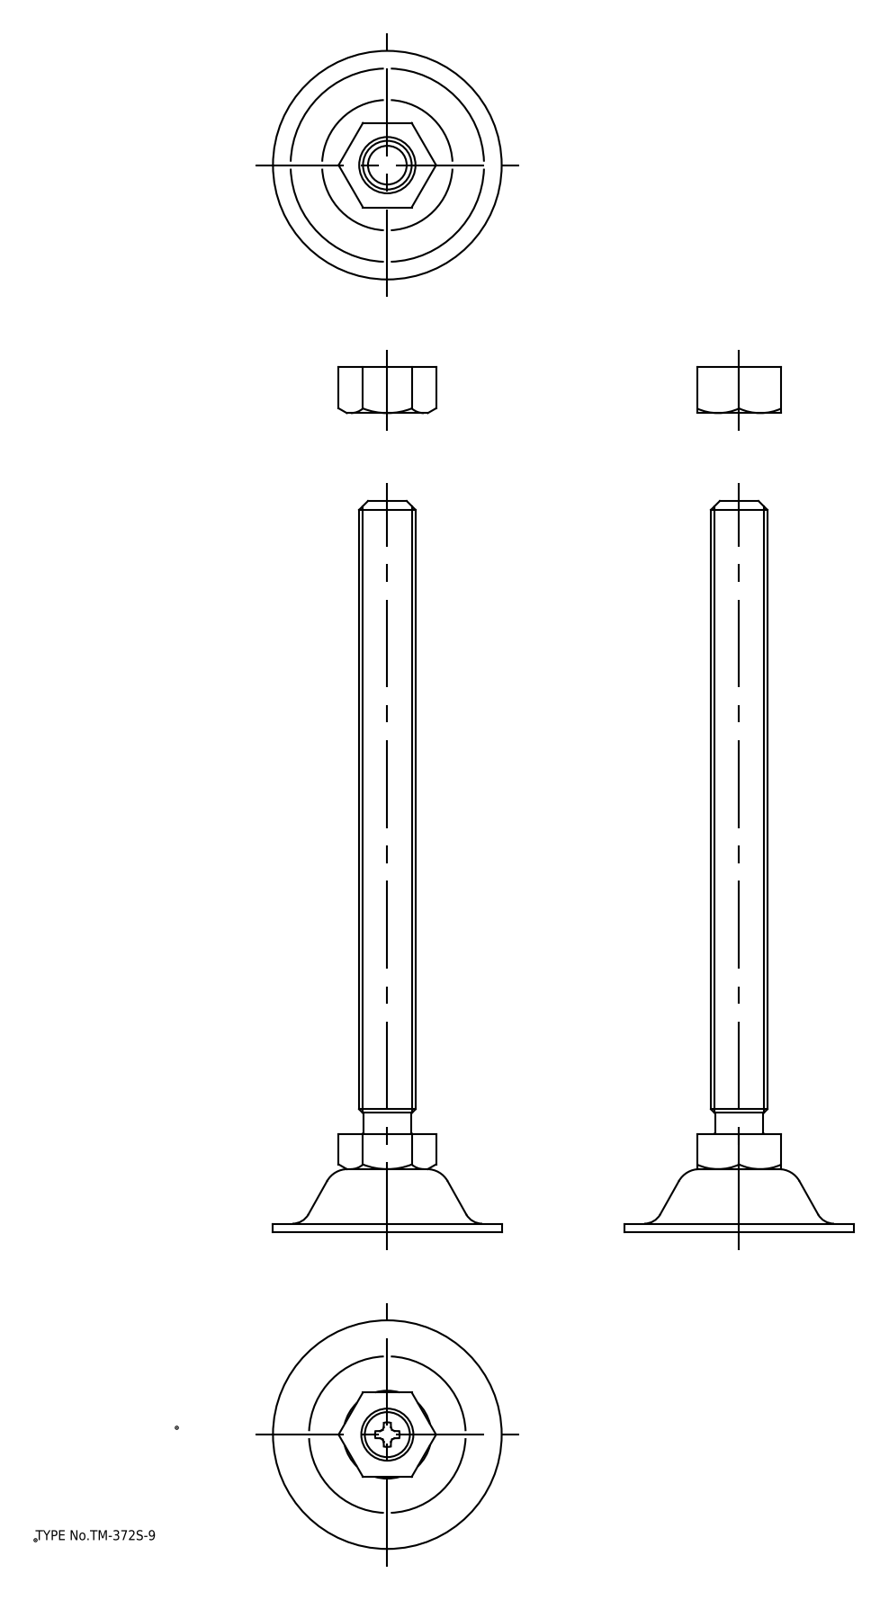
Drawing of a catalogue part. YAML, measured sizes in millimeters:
part_name: "アジャストボルト; ナット; フット"
step_written_by: "spGate 18.9.1 (****-****-****-****) (AUTOMOTIVE_DESIGN)"
units: millimeters
bodies: {solids: 3, faces: 90, planar: 48, cylindrical: 18, other: 24}
overall_size: [208, 65, 65]
volume: 59780
surface_area: 23547
round_holes:
  - {diameter: 14.8, count: 1}
  - {diameter: 16, count: 1}
round_bosses_or_shafts:
  - {diameter: 65, count: 1}
  - {diameter: 13.5, count: 1}
partial_cylinders:
  - {radius: 3.5, count: 1}
face_to_face_distances: [24, 2.5, 13, 15.5, 71.5, 4, 18, 1.5, 14, 69]
